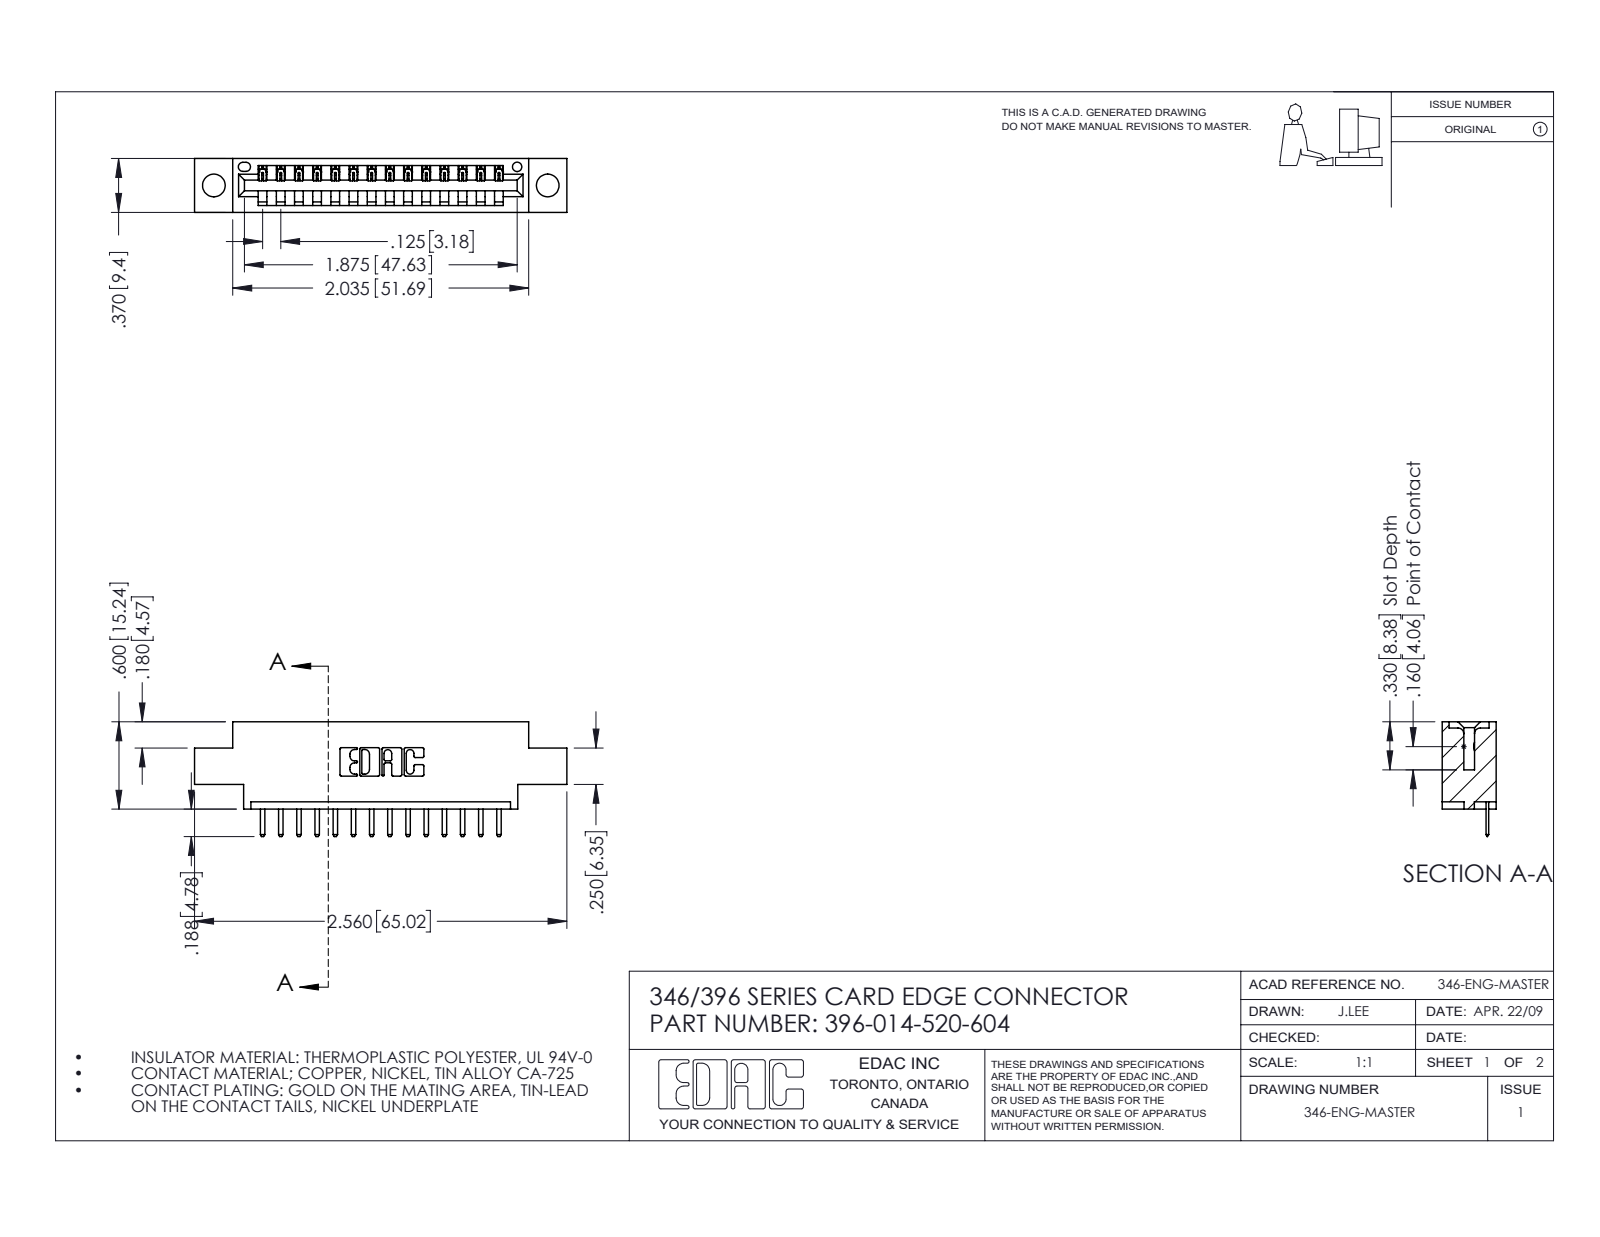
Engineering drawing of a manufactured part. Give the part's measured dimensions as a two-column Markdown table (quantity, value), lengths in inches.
| quantity | value |
| --- | --- |
| part name | 346 Part_0.170 Offset - 0.156 Dia-TH; 396-014-520-604; 345-292-001_345-293-120 |
| STEP written by | SolidWorks 2016 (CONFIG_CONTROL_DESIGN) |
| units | inches |
| bodies | 15 solids, 994 faces (668 planar, 326 cylindrical, 0 other) |
| overall size | 2.56 × 0.788 × 0.37 |
| volume | 0.351 in³ |
| surface area | 10.41 in² |
| round holes (diameter × count) | 0.156 × 2, 0.064 × 1 |
| partial cylindrical surfaces (radius × count) | 0.01 × 30, 0.006 × 28, 0.01 × 22, 0.007 × 6, 0.031 × 6, 0.026 × 3, 0.031 × 2, 0.04 × 2 |
| main face-to-face distances | 0.37, 0.048, 0.322, 0.25, 0.148, 0.222, 0.1, 0.174, 0.072, 0.298 |
| hole center spacings | 0.246, 2.089, 2.295 |
